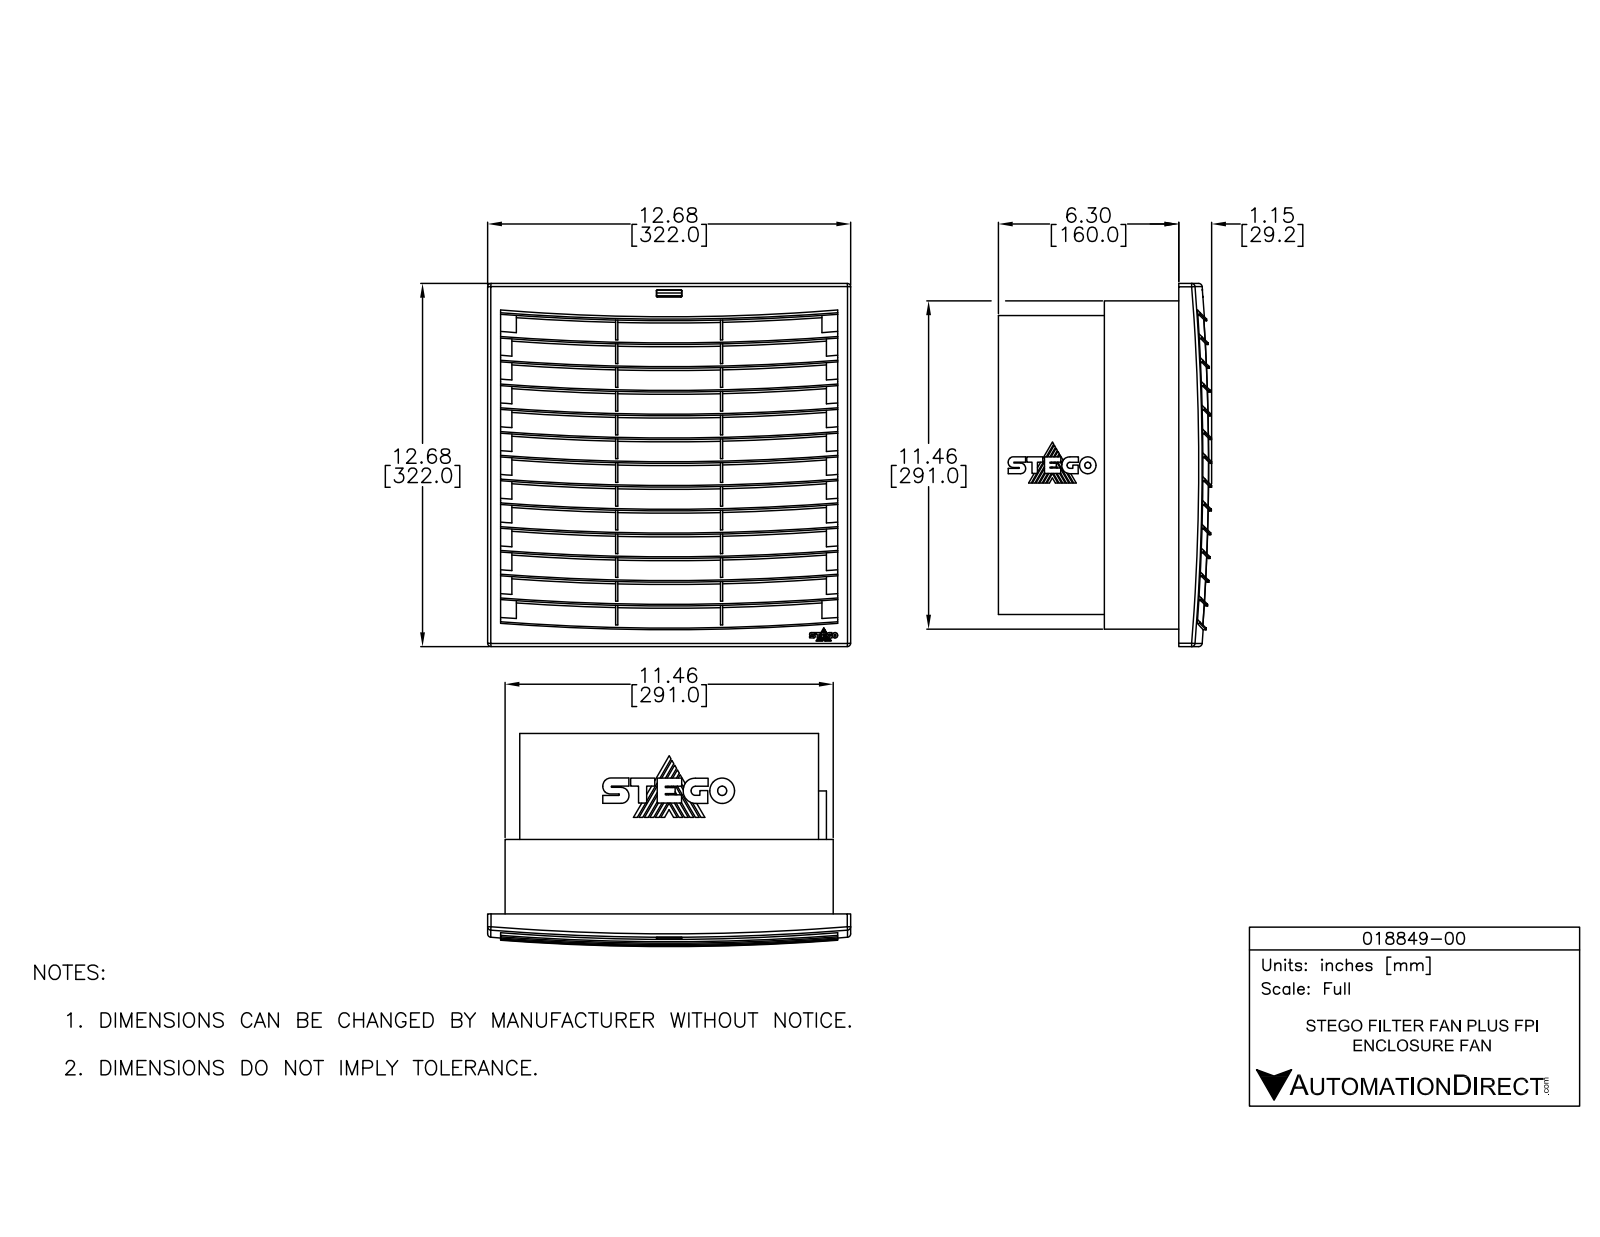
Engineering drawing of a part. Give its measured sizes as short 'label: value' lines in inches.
name: 018849-00
written by: SolidWorks 2018 (AUTOMOTIVE_DESIGN)
unit: in
bodies: 1 solid, 860 faces (506 planar, 354 cylindrical, 0 other)
size: 12.677 × 12.677 × 7.441
volume: 283.7 in³; area: 1 629 in²
holes: 1× ⌀3, 1× ⌀3.99, 1× ⌀4.692, 1× ⌀4.979, 1× ⌀5.909, 1× ⌀5.969, 1× ⌀6.958, 1× ⌀7.126, 1× ⌀7.947, 1× ⌀8.344, 1× ⌀9.134, 1× ⌀9.738
bosses: 1× ⌀11.389, 1× ⌀10.846, 1× ⌀10.738, 1× ⌀8.698, 1× ⌀8.341, 1× ⌀7.481, 1× ⌀7.352, 1× ⌀6.362
rounds: 23× R64.96, 7× R4.43, 4× R0.276, 4× R0.343, 1× R1.217, 1× R1.737, 1× R1.914, 1× R44.216
face distances: 0.059, 0.27, 0.636, 1.272, 1.909, 0.541, 2.545, 0.197, 0.811, 3.181
